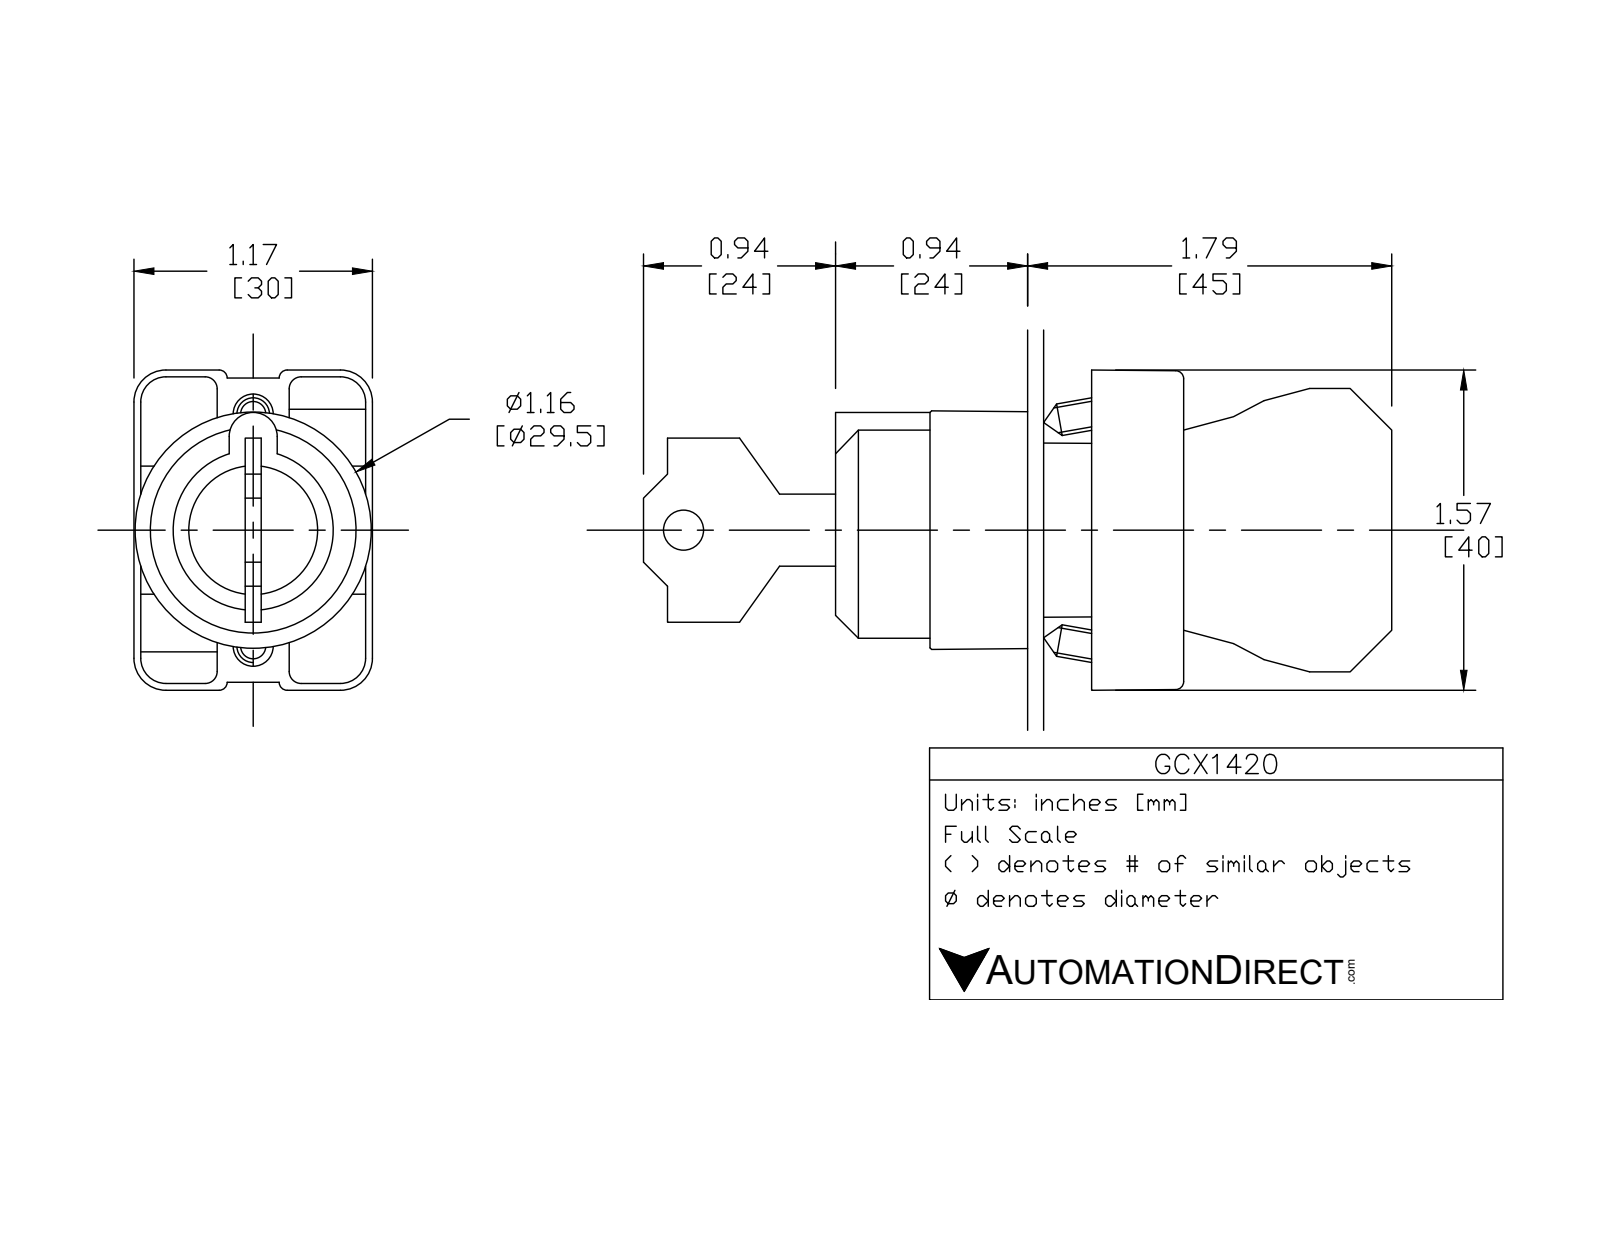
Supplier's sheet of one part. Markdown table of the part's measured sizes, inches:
| quantity | value |
| --- | --- |
| part name | ecx1029; ecx1040; GCX1420; GCX1420 OPERATOR |
| STEP written by | SolidWorks 2016 (AUTOMOTIVE_DESIGN) |
| units | inches |
| bodies | 7 solids, 405 faces (235 planar, 142 cylindrical, 28 other) |
| overall size | 2.651 × 1.581 × 1.177 |
| volume | 2.007 in³ |
| surface area | 32.29 in² |
| round holes (diameter × count) | 0.079 × 2, 0.124 × 2, 0.13 × 2, 0.087 × 1, 0.197 × 1, 0.591 × 1, 0.878 × 1, 0.888 × 1, 1.024 × 1 |
| round bosses / shafts (diameter × count) | 0.157 × 2, 1.175 × 1, 1.004 × 1, 0.965 × 1, 0.945 × 1, 0.856 × 1, 0.78 × 1, 0.571 × 1 |
| partial cylindrical surfaces (radius × count) | 0.059 × 24, 0.041 × 12, 0.124 × 12, 0.157 × 12, 0.039 × 6, 0.128 × 2, 0.02 × 1, 0.063 × 1 |
| main face-to-face distances | 0.72, 0.579, 0.033, 0.031, 0.689, 0.598, 0.539, 0.638, 0.578, 0.122 |
| hole center spacings | 0.236, 0.544, 0.472, 0.49 |
